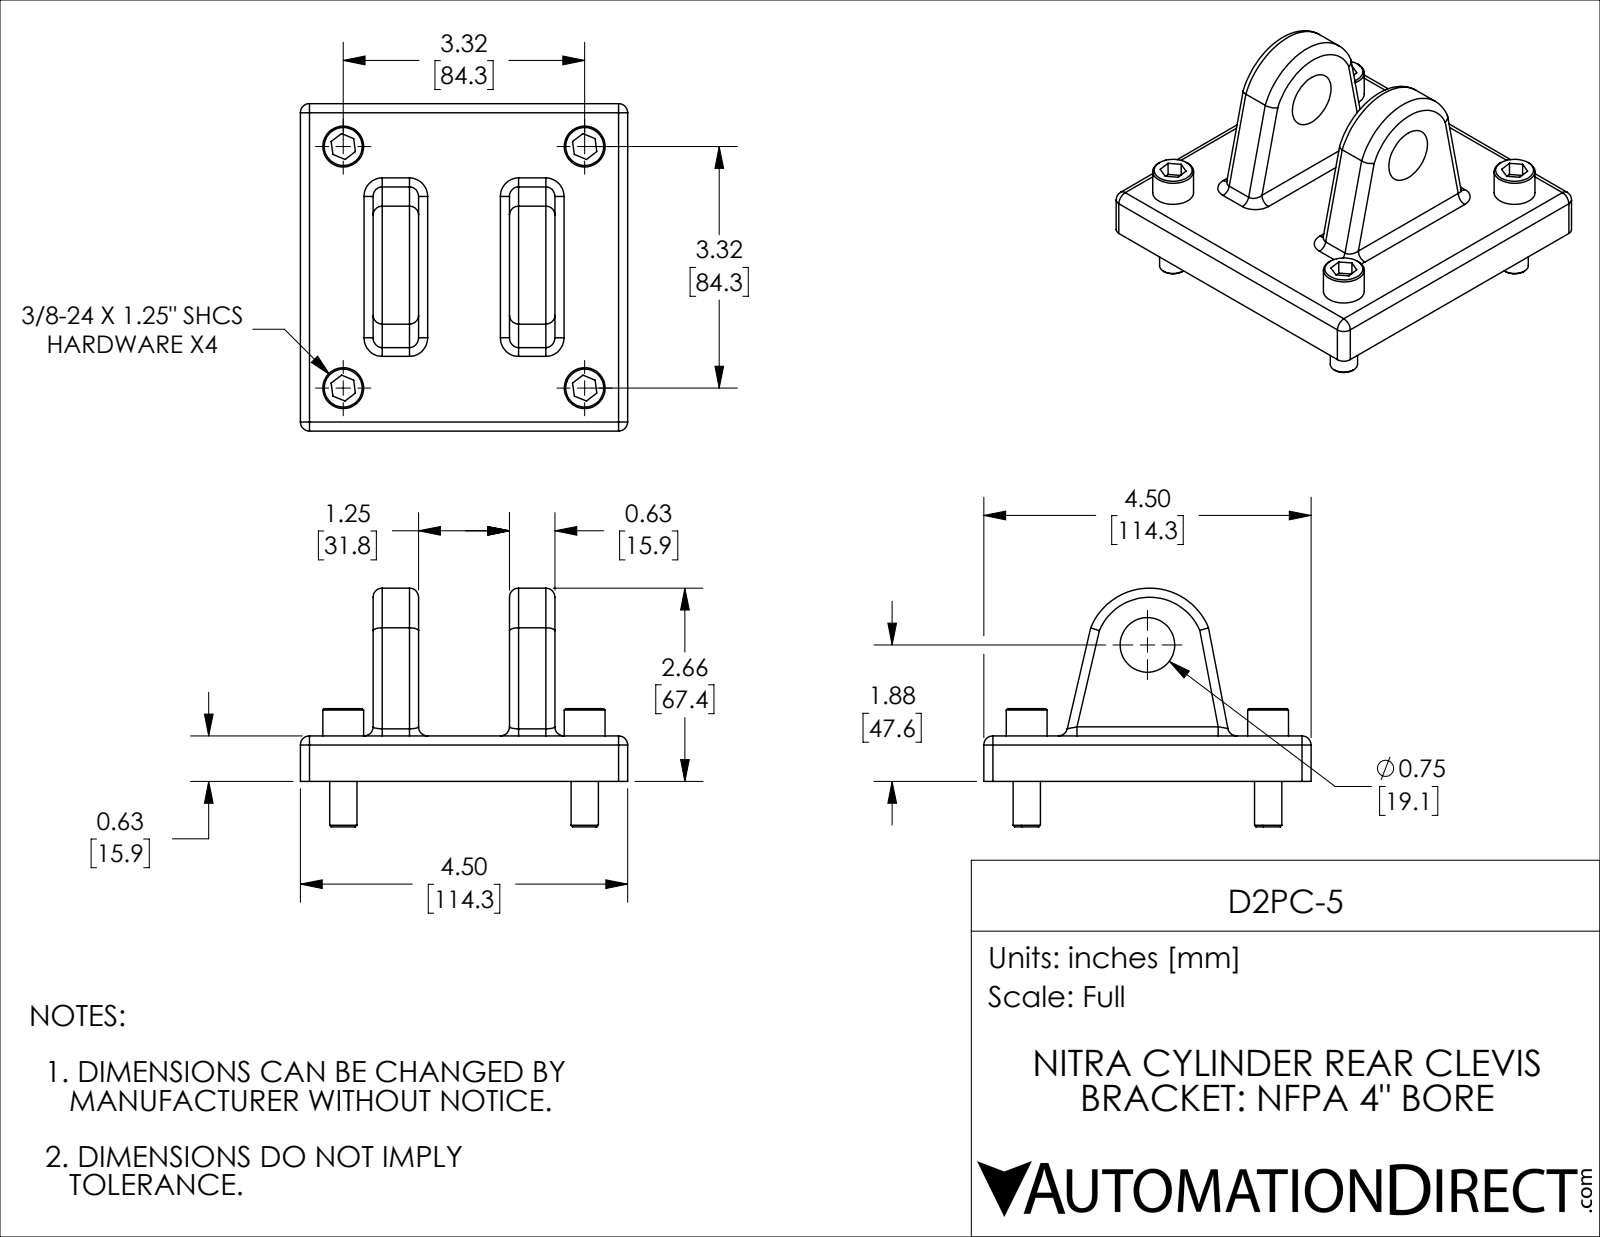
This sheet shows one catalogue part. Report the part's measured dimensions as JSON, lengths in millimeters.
{"part_name": "D2PC-5", "step_written_by": "SolidWorks 2019 (CONFIG_CONTROL_DESIGN)", "units": "millimeters", "bodies": {"solids": 5, "faces": 142, "planar": 54, "cylindrical": 54, "other": 34}, "overall_size": [114.3, 114.3, 83.3], "volume_mm3": 277400, "surface_area_mm2": 52370, "round_holes": [[10.3, 4], [19.1, 1]], "round_bosses_or_shafts": [[14.3, 4], [9.5, 4]], "partial_cylinders_radius": [[3.2, 22], [22.2, 1]], "face_to_face_distances": [15.9, 15.9, 47.6, 25.4, 41.3, 73, 88.9, 114.3, 63.5, 31.8], "hole_center_spacings": [84.3, 119.3]}
